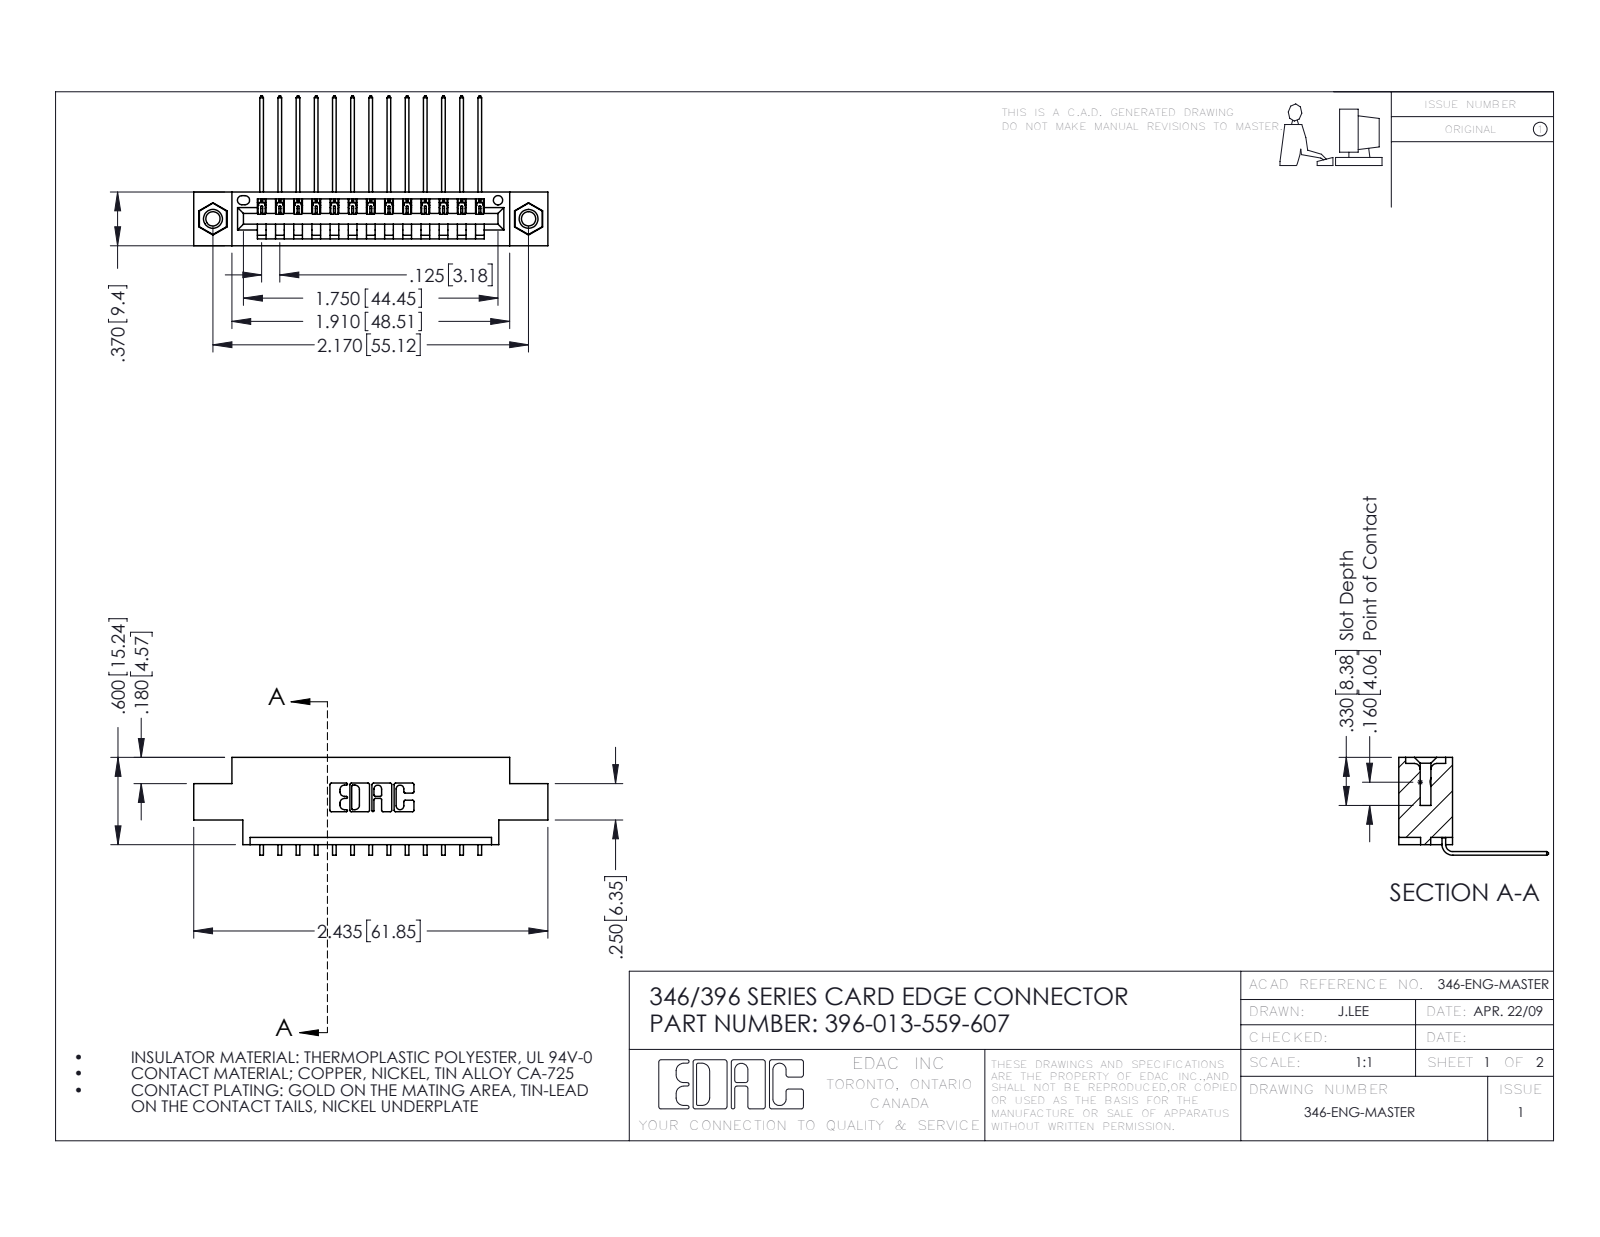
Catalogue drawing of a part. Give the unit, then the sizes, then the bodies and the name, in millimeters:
Units: millimetres
Overall size (bounding box): 61.8 × 26.2 × 17.1
Round holes (diameter × count): ⌀2.5 ×2, ⌀3.2 ×2, ⌀4 ×2, ⌀1.6 ×1
Round bosses / shafts (diameter × count): ⌀3.9 ×2
Partial cylindrical surfaces — rounded edges, fillets, slot ends (radius × count): R0.2 ×26, R0.3 ×22, R0.2 ×6, R0.8 ×6, R0.7 ×3, R0.8 ×2, R1 ×2, R0.4 ×1
Main face-to-face distances: 1.2, 9.4, 6.4, 8.2, 0.6, 1.8, 5.6, 3.8, 2.5, 4.4
Hole centre spacings: 6.2, 49.9, 55.1
Volume: 5 590 mm³ · Surface area: 7 135 mm²
Bodies: 16 solids, 966 faces (658 planar, 292 cylindrical, 16 other)
Part name (STEP PRODUCT): 396-013-559-607; 345-292-001_558 559 Tail - 1; 346 Part_0.170 Offset - 0.156 Dia-TI; 345-250-001_345-250-005-103
STEP written by: SolidWorks 2016 (CONFIG_CONTROL_DESIGN)
